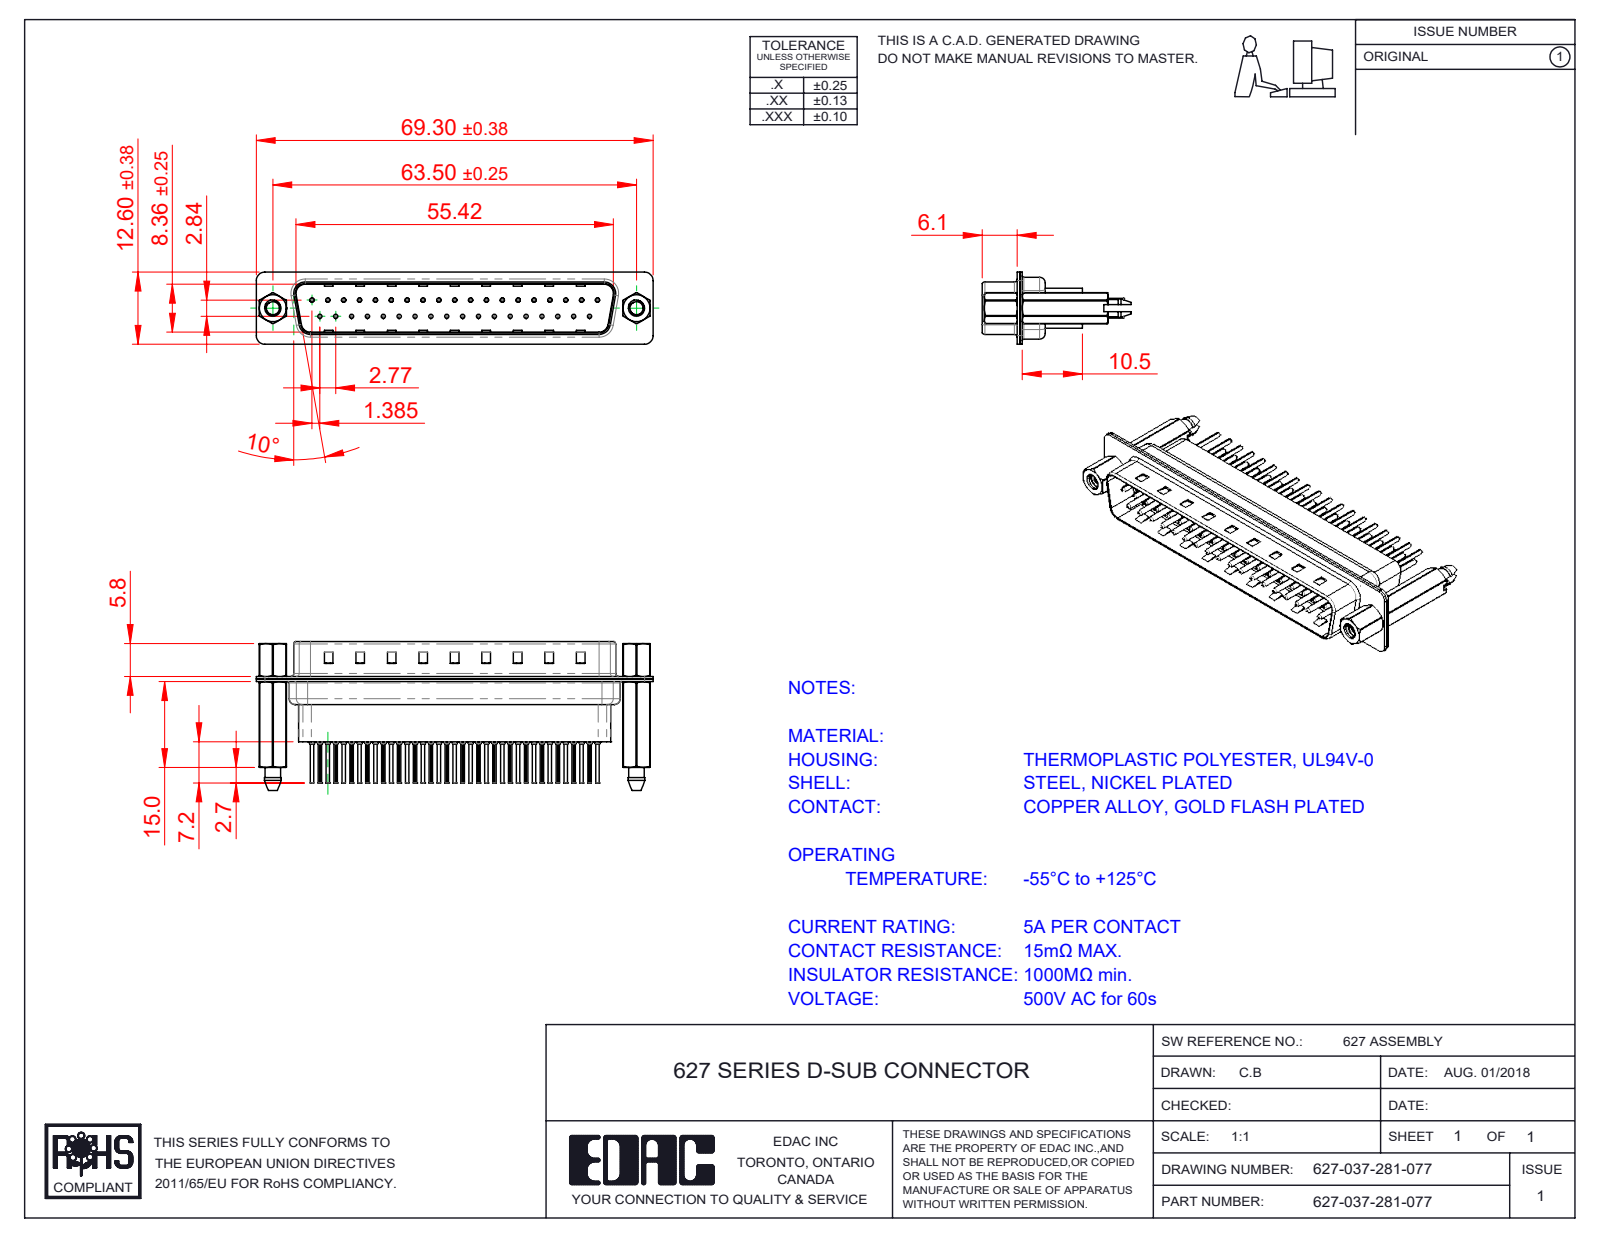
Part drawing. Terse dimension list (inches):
name: 627 4-40 Hex Standoff; 627 Contact Row 2_61; 627 Shell Rear_37 Contacts; 627 Shell Front_37 Contacts (+4 more)
written by: SolidWorks 2020 (CONFIG_CONTROL_DESIGN)
unit: in
bodies: 44 solids, 4272 faces (1145 planar, 1648 cylindrical, 1479 other)
size: 2.728 × 1.02 × 0.496
volume: 0.362 in³; area: 23.6 in²
holes: 37× ⌀0.008, 37× ⌀0.014, 37× ⌀0.043, 37× ⌀0.063, 2× ⌀0.089, 2× ⌀0.09, 2× ⌀0.157, 2× ⌀0.189
bosses: 37× ⌀0.079, 37× ⌀0.059, 37× ⌀0.03, 37× ⌀0.024, 2× ⌀0.193, 2× ⌀0.11
rounds: 74× R0.004, 18× R0.059, 12× R0.079, 10× R0.063, 8× R0.02, 4× R0.01, 4× R0.024, 4× R0.026
face distances: 0.016, 0.032, 0.377, 0.018, 0.027, 0.302, 0.059, 0.043, 0.318, 0.345
hole spacings: 0.124, 0.109, 0.218, 0.327, 0.198, 0.398, 0.436, 0.503
